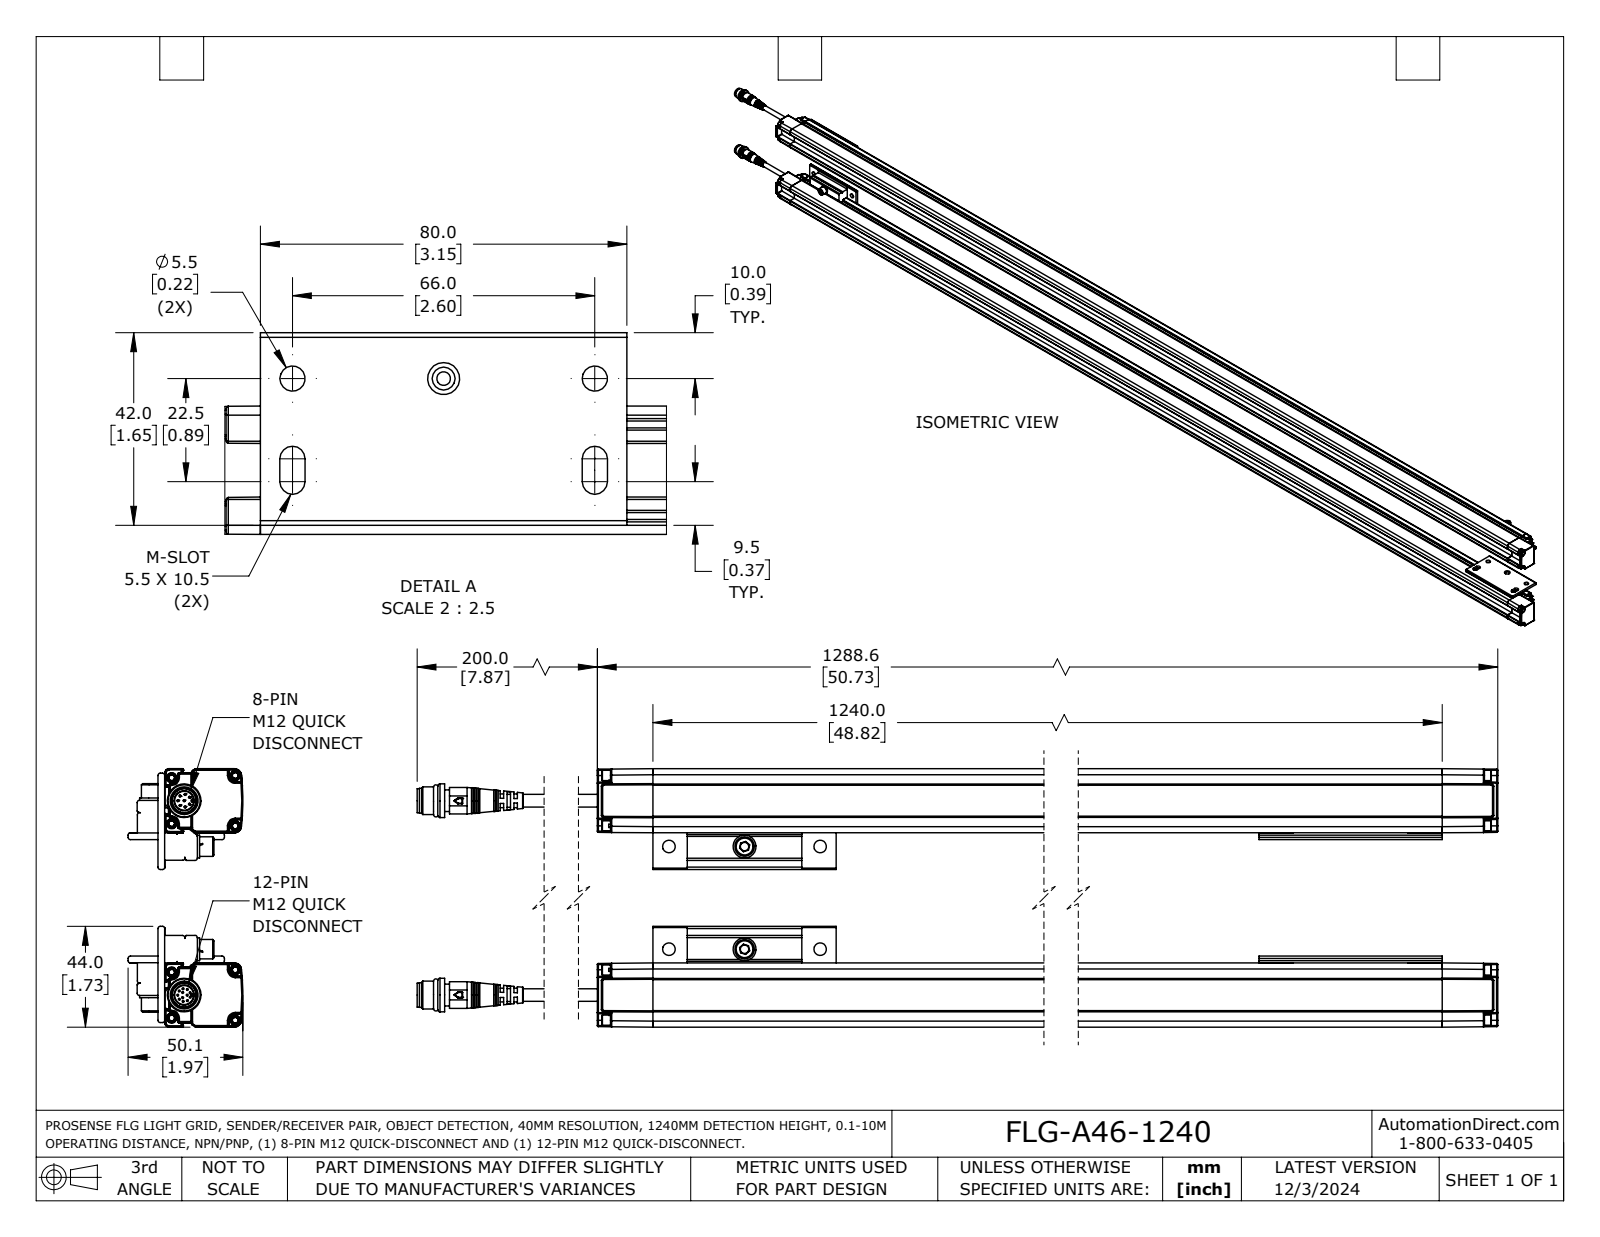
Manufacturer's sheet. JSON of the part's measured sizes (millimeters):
{"part_name": "FLG-A46-1240", "step_written_by": "SolidWorks 2023 (AUTOMOTIVE_DESIGN)", "units": "millimeters", "bodies": {"solids": 5, "faces": 869, "planar": 435, "cylindrical": 238, "other": 196}, "overall_size": [1380.5, 50.1, 44], "volume_mm3": 1036000, "surface_area_mm2": 254300, "round_holes": [[0.4, 16], [5.5, 4], [2.5, 2], [5, 2], [8.3, 1]], "round_bosses_or_shafts": [[0.8, 8], [4.5, 4], [3, 4], [10, 2], [8.5, 2], [5.5, 2], [3.7, 2], [1.5, 2]], "partial_cylinders_radius": [[0.5, 76], [1, 20], [0.3, 10], [2.7, 8], [0.2, 6], [0.3, 6], [2.5, 4], [1.2, 2]], "face_to_face_distances": [28, 1.8, 20.8, 7.2, 24.6, 26.4, 5.5, 26.2, 18.9, 13.5], "hole_center_spacings": [2.7, 4.1, 33, 5.5, 2.3, 2.3, 2.3, 3]}
